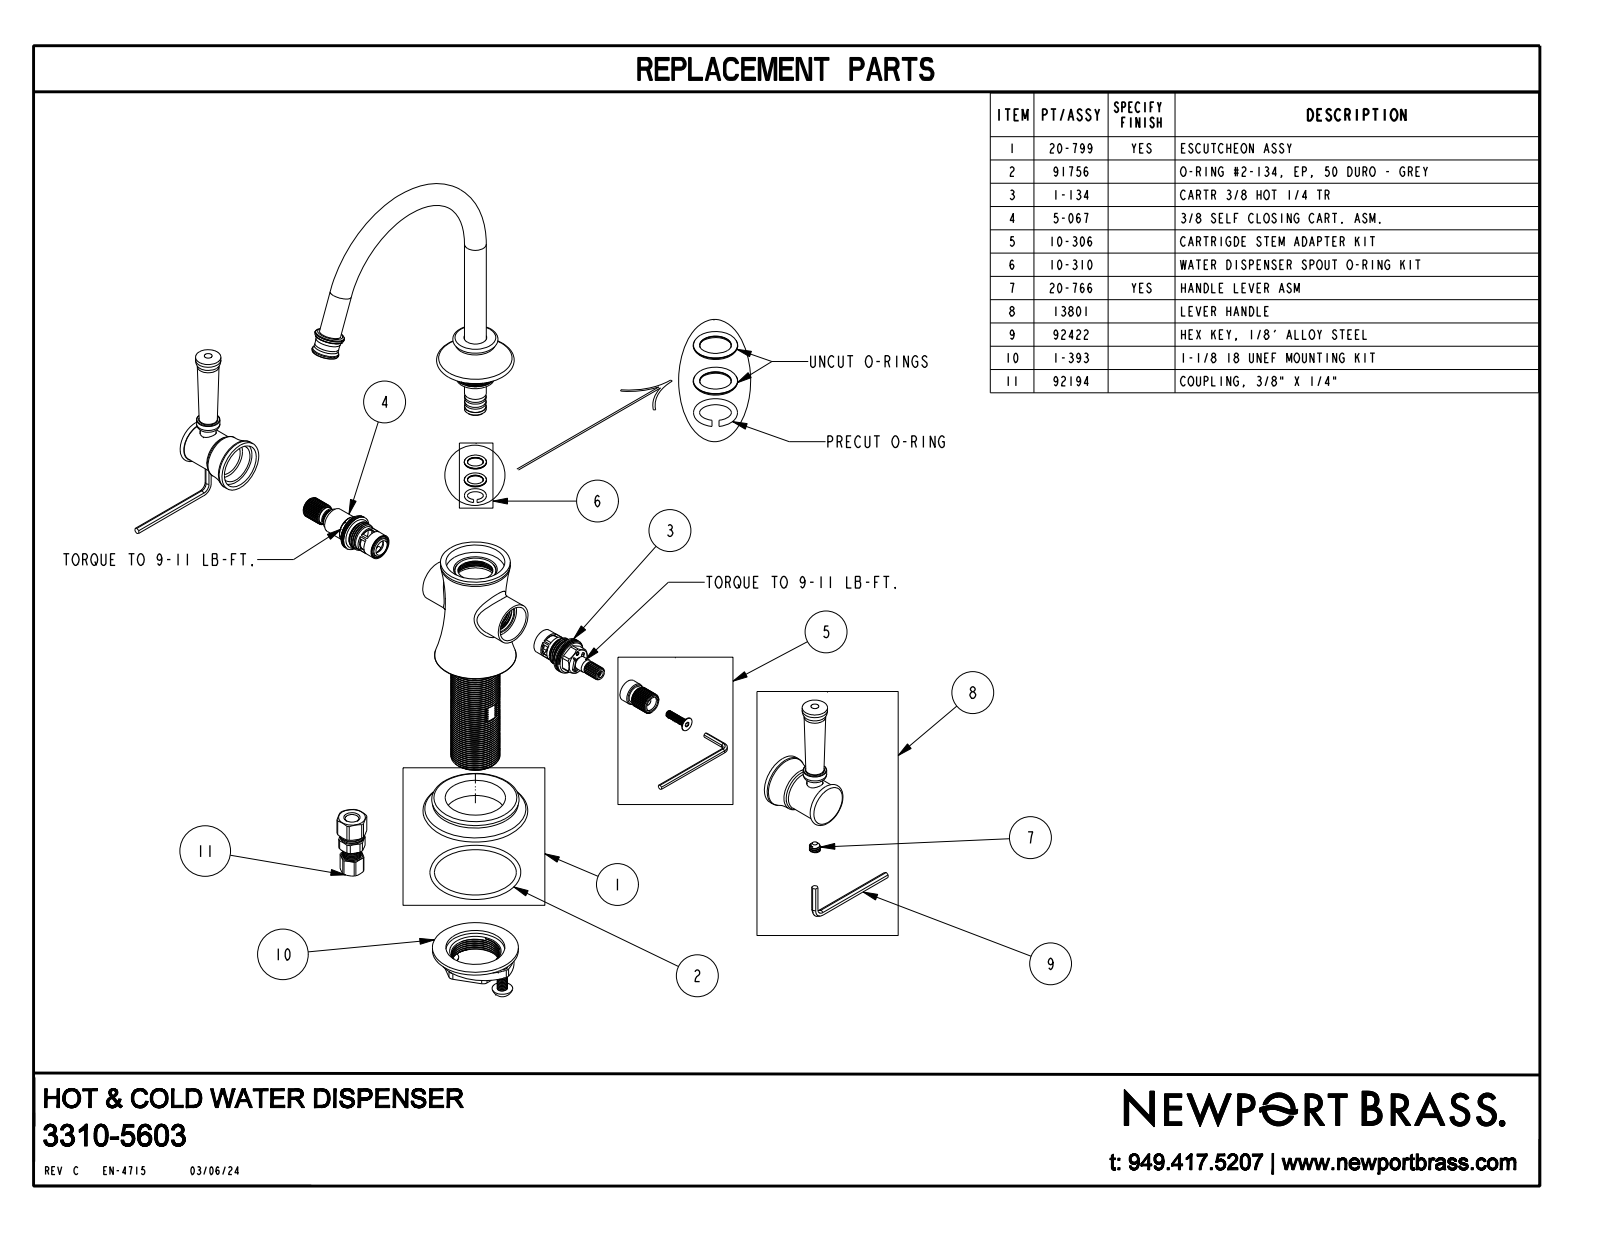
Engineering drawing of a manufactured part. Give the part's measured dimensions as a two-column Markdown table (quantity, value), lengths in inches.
| quantity | value |
| --- | --- |
| part name | 3310-5603 |
| STEP written by | CREO PARAMETRIC BY PTC INC, 2018400 (CONFIG_CONTROL_DESIGN) |
| units | inches |
| bodies | 1 solid, 168 faces (22 planar, 40 cylindrical, 106 other) |
| overall size | 9.75 × 6.232 × 5.196 |
| volume | 12.87 in³ |
| surface area | 66.48 in² |
| round holes (diameter × count) | 0.375 × 2, 0.52 × 1, 1.64 × 1 |
| round bosses / shafts (diameter × count) | 0.58 × 2, 0.536 × 2, 0.5 × 2, 0.36 × 2, 1.6 × 1, 1.19 × 1, 1 × 1, 0.96 × 1 |
| main face-to-face distances | 3.07, 0.02, 3.05, 1.47, 3.726, 5.196, 3.725, 0.675, 0.655, 2.256 |
| hole center spacings | 2.17, 4.339 |
